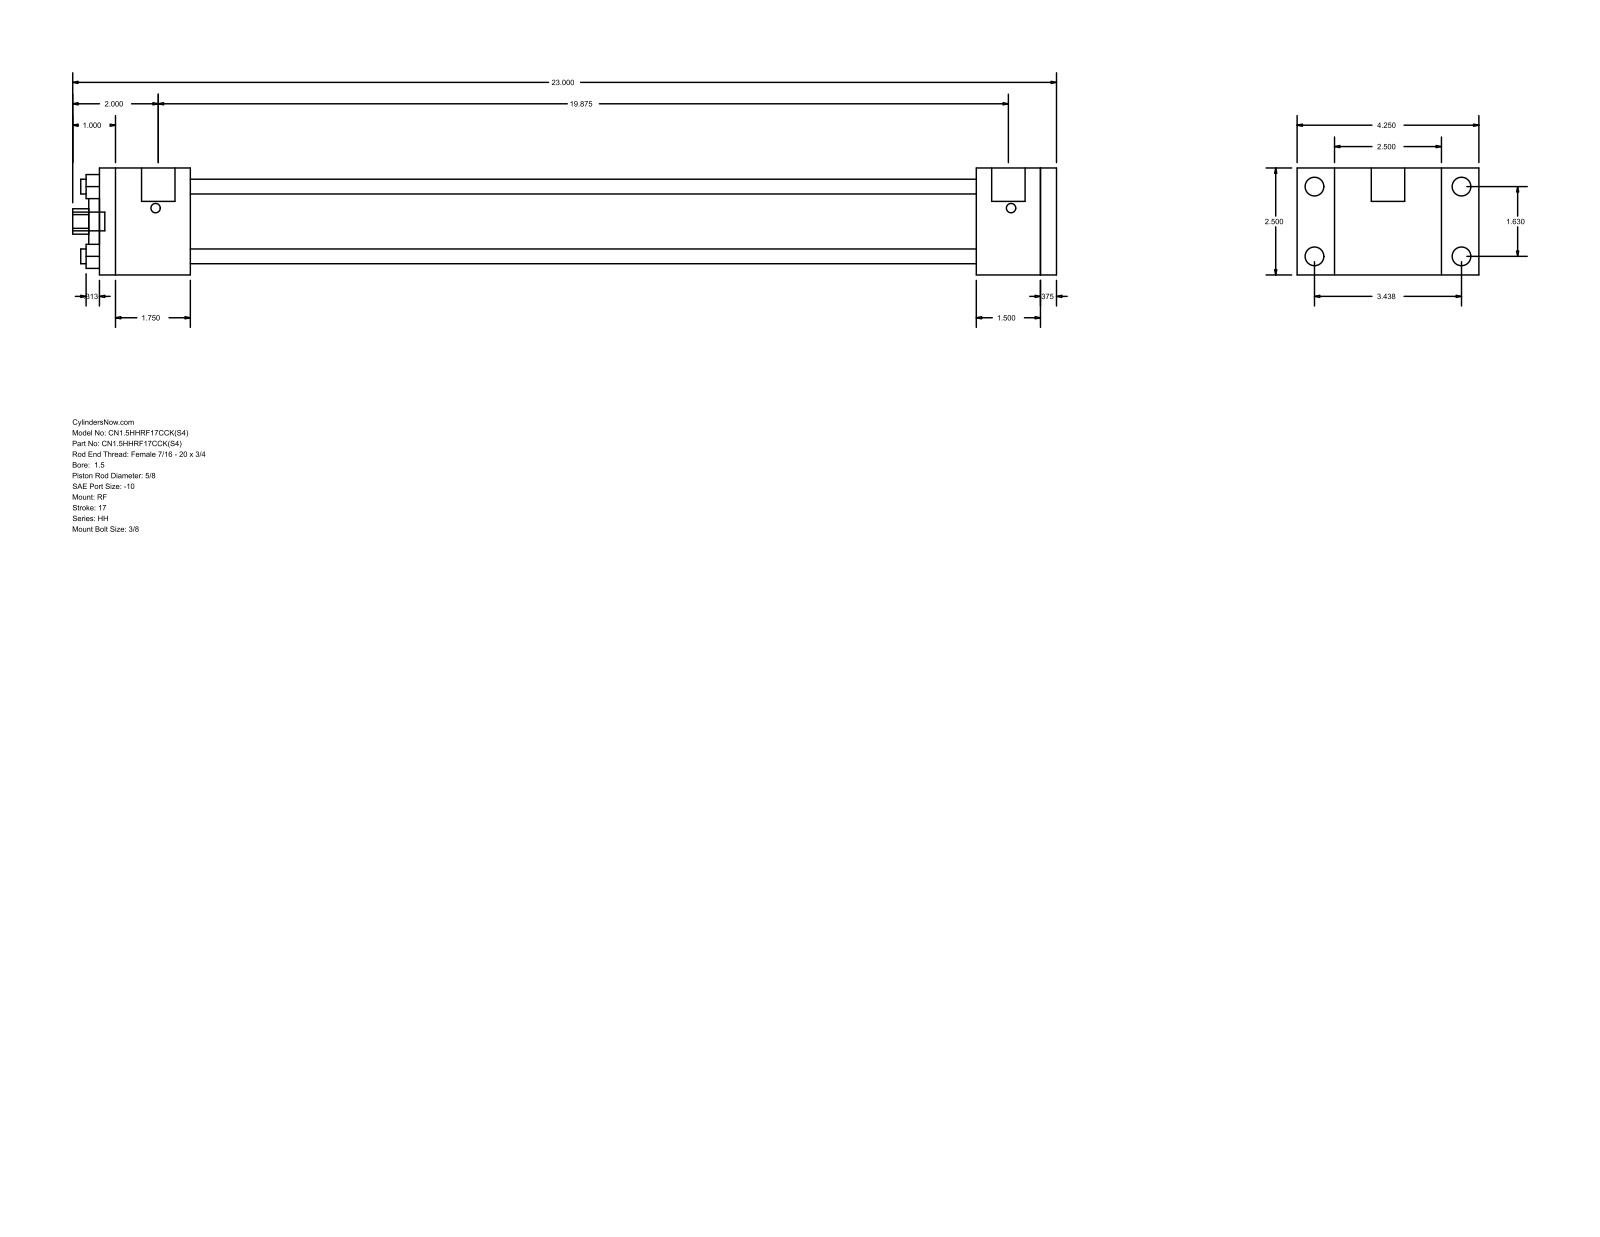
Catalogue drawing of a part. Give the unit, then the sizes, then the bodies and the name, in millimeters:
Units: millimetres
Overall size (bounding box): 584.2 × 107.95 × 63.5
Round holes (diameter × count): ⌀8.76 ×4, ⌀15.88 ×1, ⌀28.57 ×1, ⌀44.45 ×1
Round bosses / shafts (diameter × count): ⌀11.13 ×4, ⌀5.56 ×4, ⌀19.84 ×2, ⌀11.11 ×1
Partial cylindrical surfaces — rounded edges, fillets, slot ends (radius × count): R7.54 ×1
Main face-to-face distances: 63.5, 568.32, 9.53, 558.79, 53.97, 520.7, 466.73, 504.82, 514.35, 38.09
Hole centre spacings: 29.27, 41.4, 58.55
Bodies: 0 solids, 92 faces (64 planar, 28 cylindrical, 0 other)
Part name (STEP PRODUCT): HH_RF__0150_0.625
STEP written by: GSSL Pune (CONFIG_CONTROL_DESIGN)
